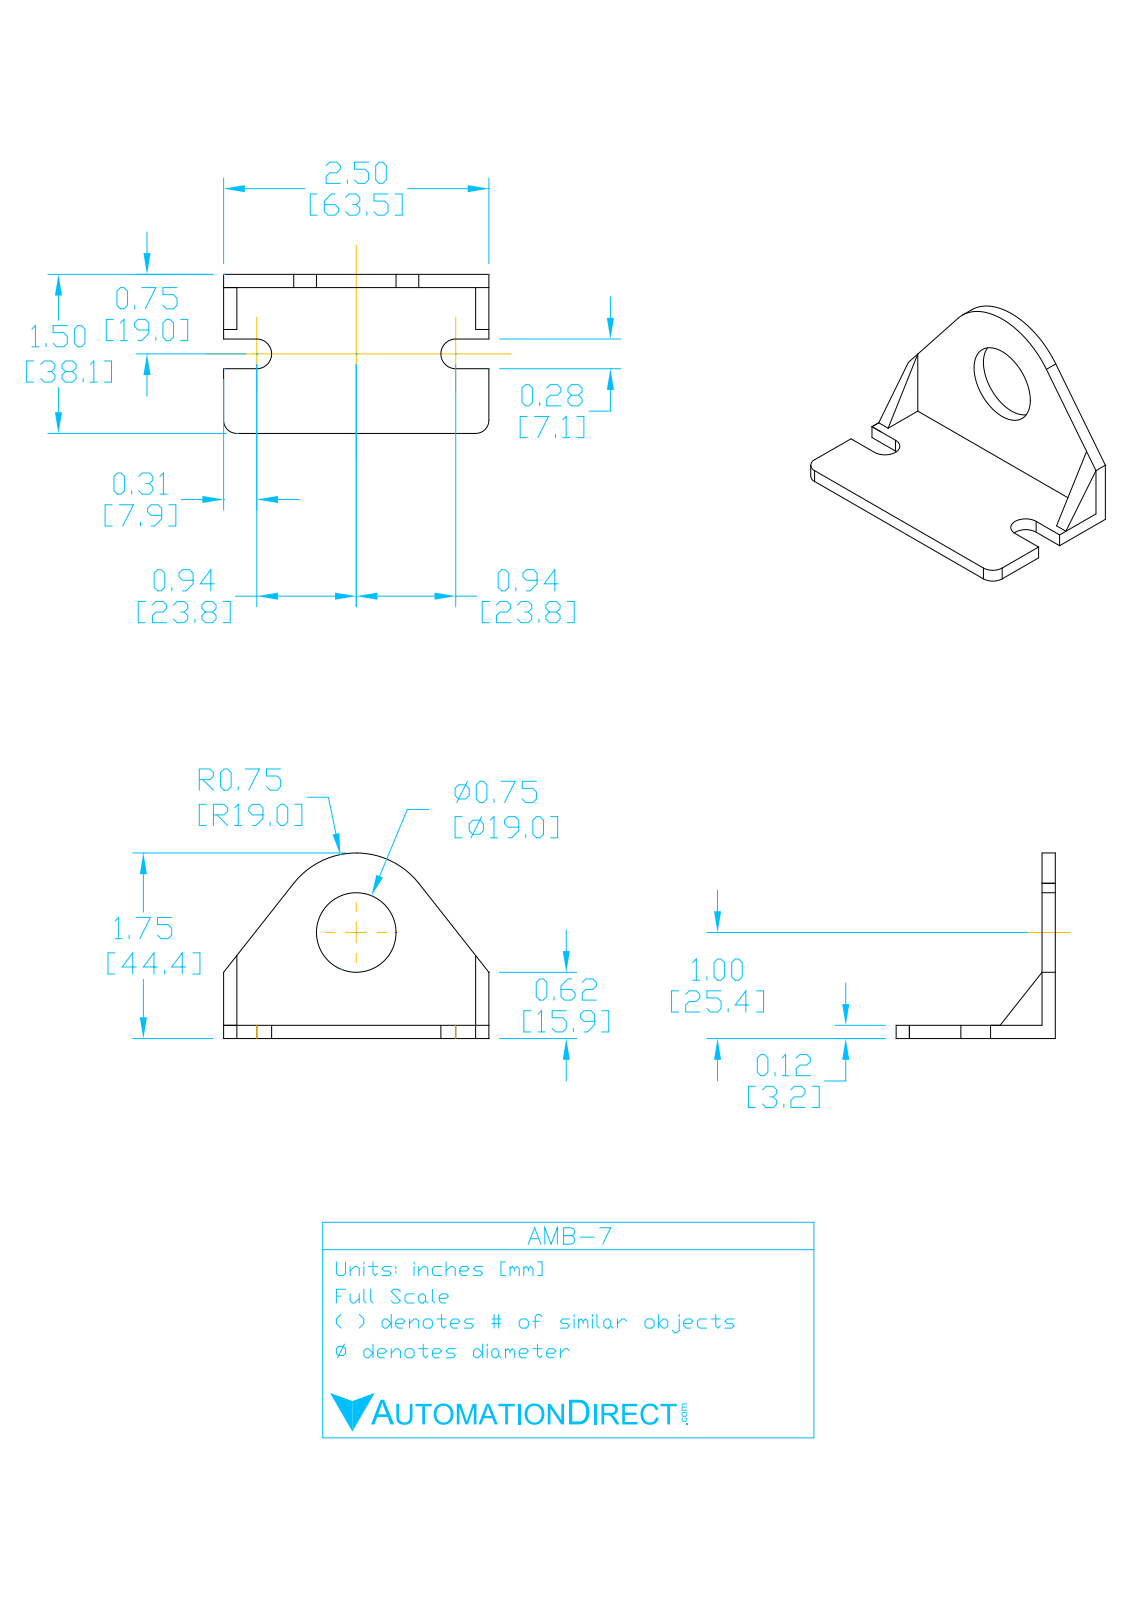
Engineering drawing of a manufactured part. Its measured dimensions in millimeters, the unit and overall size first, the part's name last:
Units: millimetres
Overall size (bounding box): 63.5 × 44.5 × 38.1
Round holes (diameter × count): ⌀19.1 ×1
Partial cylindrical surfaces — rounded edges, fillets, slot ends (radius × count): R3.6 ×2, R4.7 ×2, R1.5 ×1, R4.7 ×1, R19.1 ×1
Main face-to-face distances: 3.2, 3.2, 63.5, 34.9, 38.1, 2.5, 61, 15.5, 22.6, 58.4
Volume: 12 500 mm³ · Surface area: 9 006 mm²
Bodies: 1 solid, 28 faces (19 planar, 9 cylindrical, 0 other)
Part name (STEP PRODUCT): AMB-7
STEP written by: SolidWorks 2017 (AUTOMOTIVE_DESIGN)
